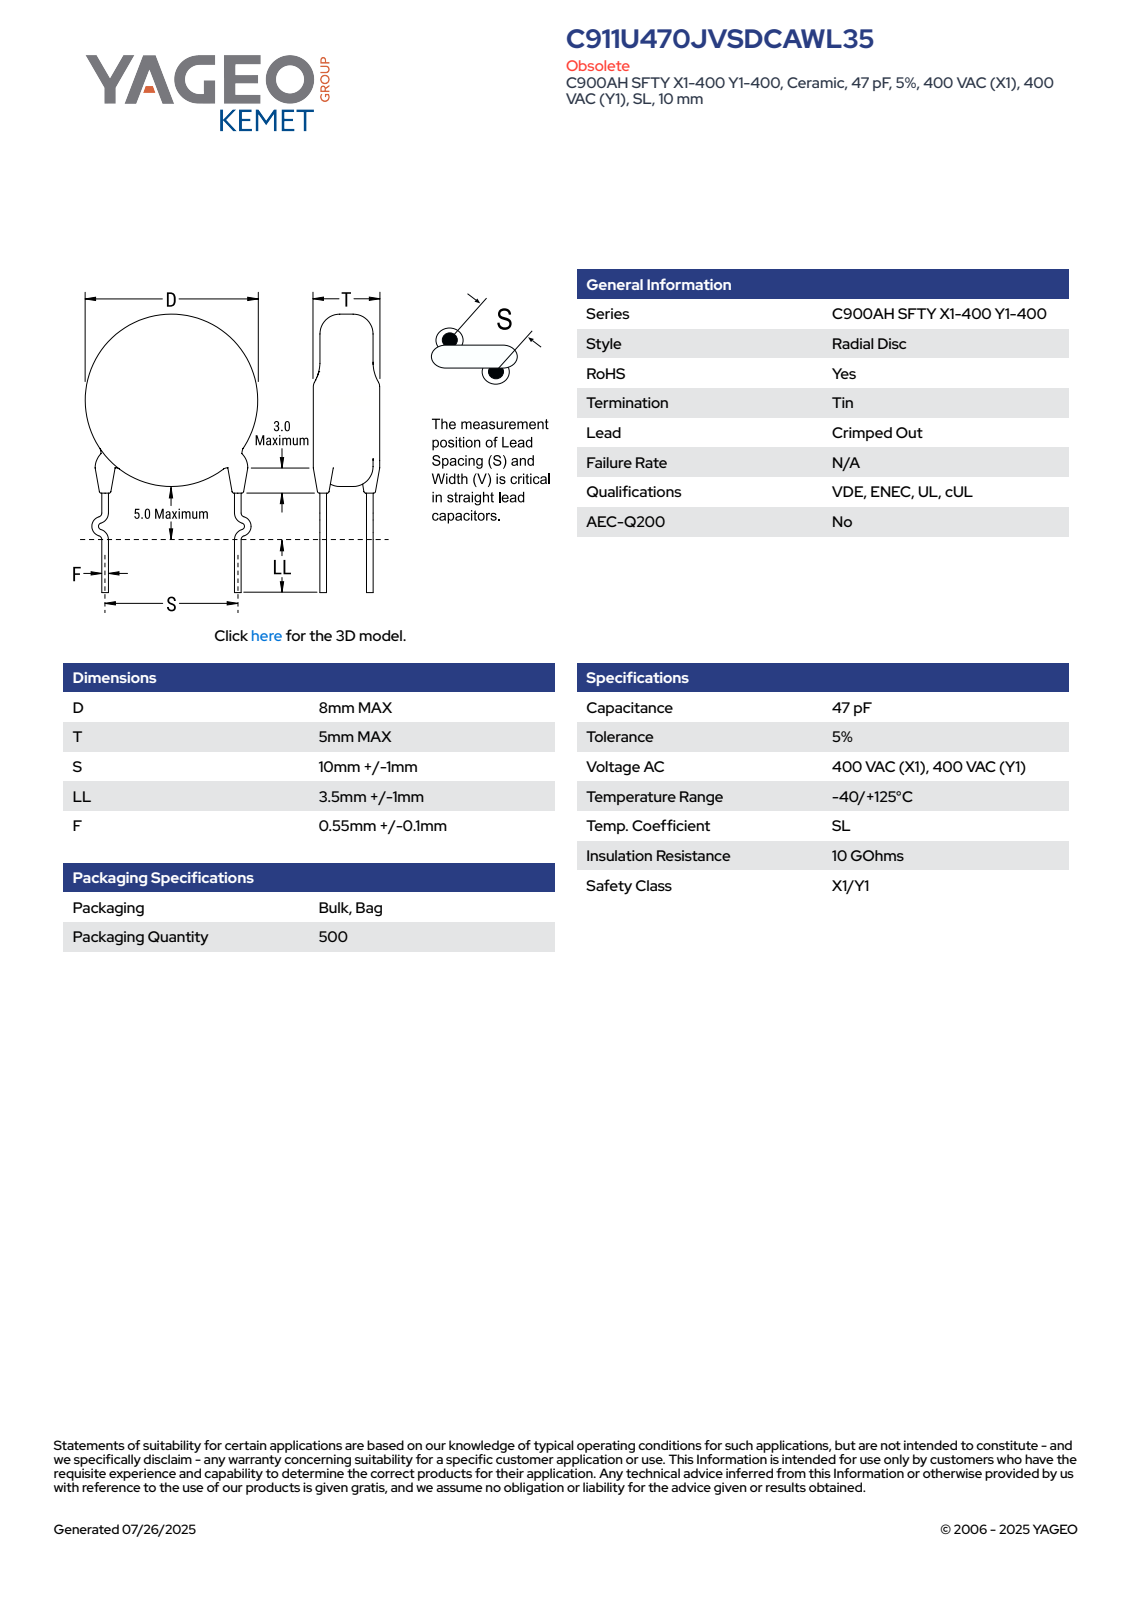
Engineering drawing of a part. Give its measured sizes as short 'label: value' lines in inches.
name: CCD_KCOC900_D8T5S10LL4.5F0.55
written by: SolidWorks 2014 (AUTOMOTIVE_DESIGN)
unit: in
bodies: 4 solids, 93 faces (63 planar, 10 cylindrical, 20 other)
size: 0.689 × 0.561 × 0.249
volume: 0.016 in³; area: 0.436 in²
bosses: 4× ⌀0.047, 1× ⌀0.315
face distances: 0.197, 0.033, 0.174, 0.141, 0.133, 0.02, 0.012, 0.026, 0.067, 0.097
